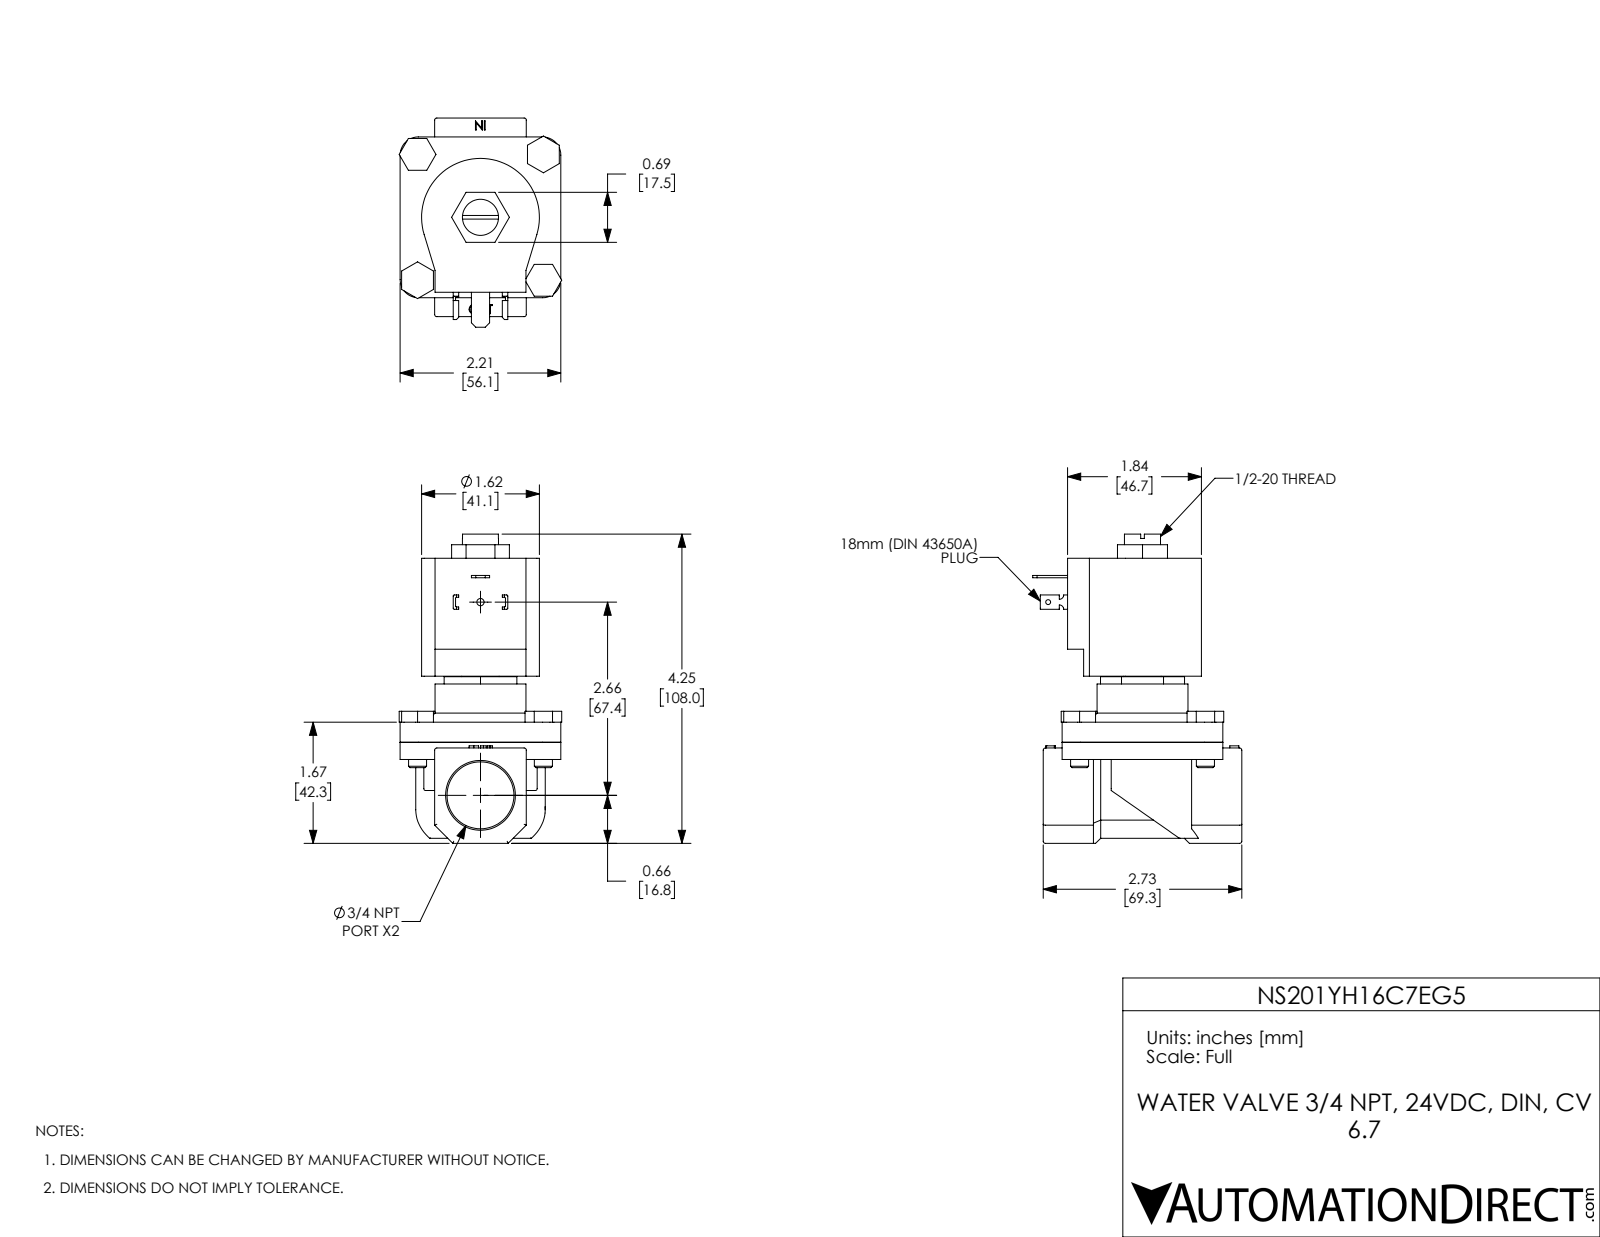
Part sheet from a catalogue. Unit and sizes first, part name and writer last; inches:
Units: inches
Overall size (bounding box): 4.25 × 2.875 × 2.235
Round holes (diameter × count): ⌀0.25 ×4, ⌀0.067 ×1, ⌀0.1 ×1, ⌀0.496 ×1, ⌀0.512 ×1, ⌀0.92 ×1, ⌀1.155 ×1
Round bosses / shafts (diameter × count): ⌀0.248 ×4, ⌀1.25 ×1
Partial cylindrical surfaces — rounded edges, fillets, slot ends (radius × count): R0.03 ×15, R0.015 ×8, R0.25 ×4, R0.06 ×2, R0.81 ×1, R0.89 ×1
Main face-to-face distances: 0.276, 2.529, 2.253, 0.475, 1.735, 2.21, 0.236, 0.512, 2.765, 0.26
Hole centre spacings: 1.223, 1.73, 2.446, 2.656
Volume: 10.35 in³ · Surface area: 67.29 in²
Bodies: 11 solids, 332 faces (198 planar, 99 cylindrical, 35 other)
Part name (STEP PRODUCT): NS201YH16C7EG5
STEP written by: SolidWorks 2024 (CONFIG_CONTROL_DESIGN)
